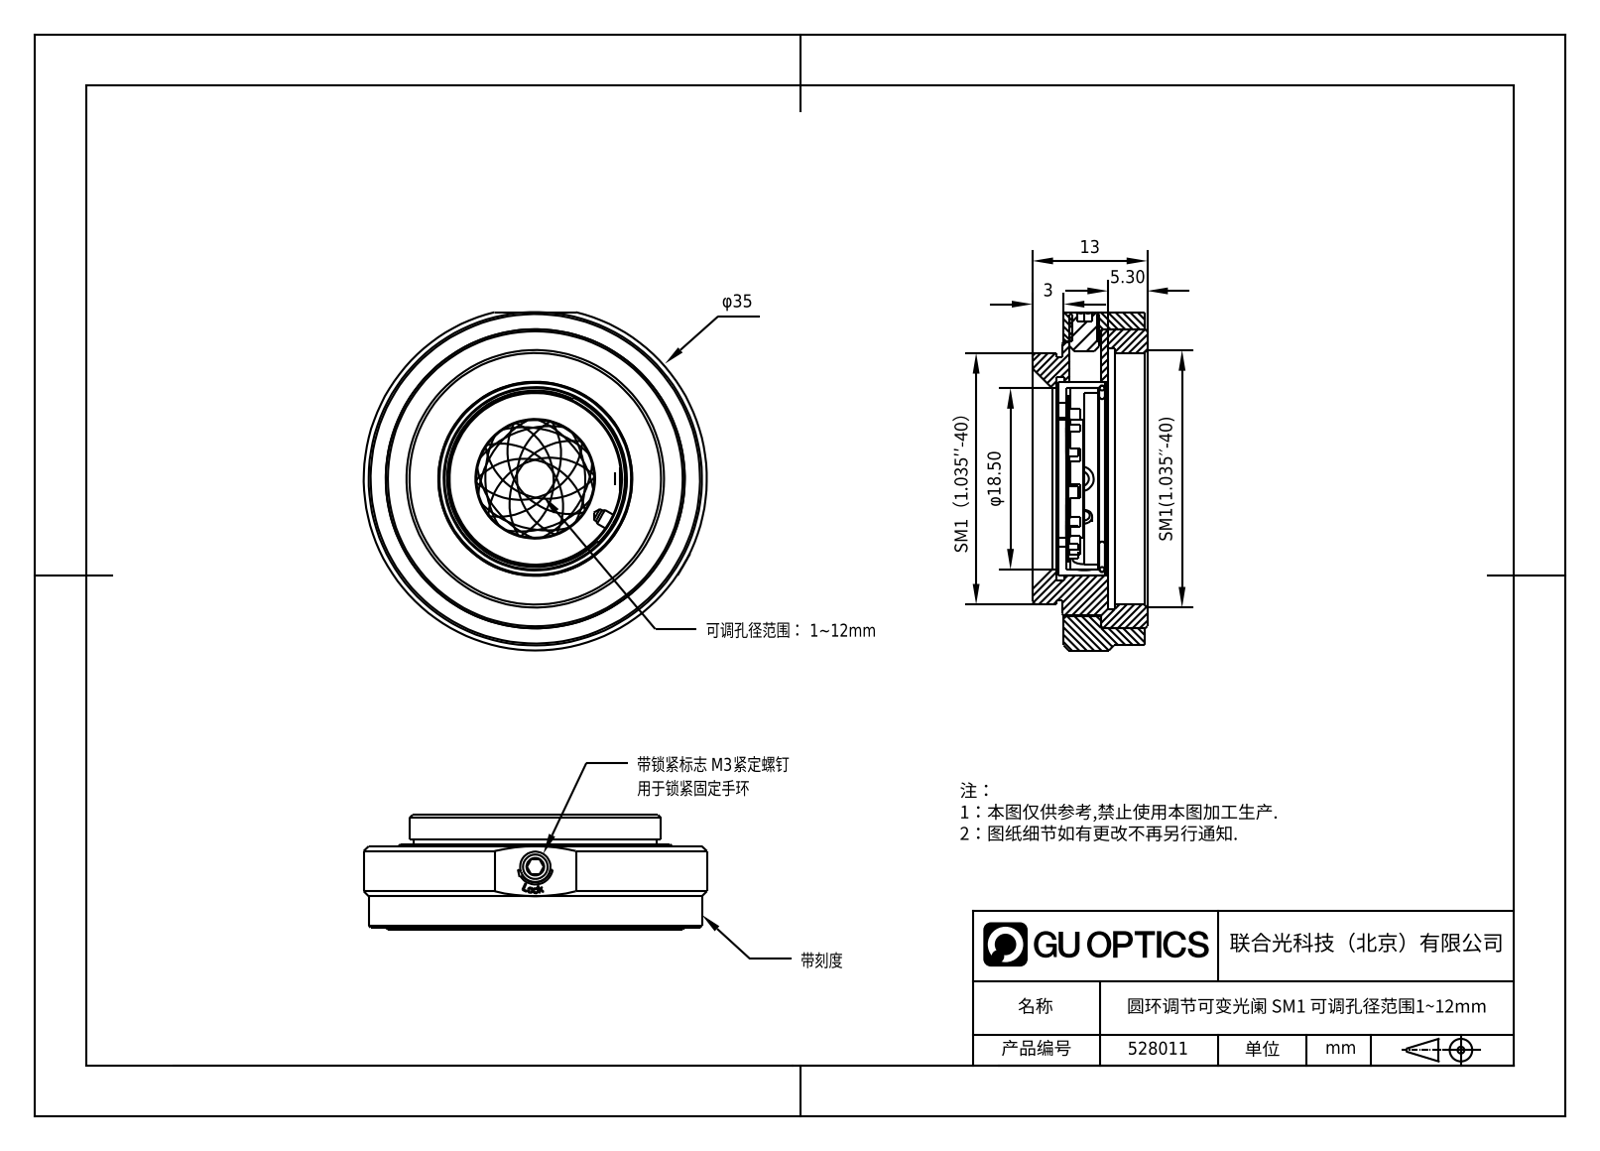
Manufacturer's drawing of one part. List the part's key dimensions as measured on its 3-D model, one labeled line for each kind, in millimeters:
Part name (STEP PRODUCT): SM1螺纹圆环式可调光阑手环，外径35mm，零部件_1.5.2.7.1_ZXL-H1D12B; 1.5.2.7.2_SM1螺纹分度圆环式可调光阑主体，带SM1内外螺纹，外径35mm，零部件，Rev.A; 30.8.1-7，M3尼龙头顶丝_30.8.1_LNJ3*3; 30.5.87-93，LPJ2.5，M2.5不锈钢平头紧定螺丝_30.5.88-PJ2.5*4 (+1 more)
STEP written by: SolidWorks 2021 (CONFIG_CONTROL_DESIGN)
Units: millimetres
Bodies: 4 solids, 1806 faces (256 planar, 384 cylindrical, 1166 other)
Overall size (bounding box): 36.96 × 35 × 13
Volume: 5 097 mm³ · Surface area: 8 851 mm²
Round holes (diameter × count): ⌀1.5 ×2, ⌀1.25 ×1, ⌀2.05 ×1, ⌀2.5 ×1, ⌀2.8 ×1, ⌀12 ×1, ⌀17.5 ×1, ⌀18.5 ×1, ⌀19.8 ×1, ⌀20.8 ×1, ⌀25.66 ×1, ⌀26.66 ×1
Round bosses / shafts (diameter × count): ⌀1.5 ×18, ⌀2 ×2, ⌀35 ×1, ⌀34 ×1, ⌀27.9 ×1, ⌀24.86 ×1, ⌀19.75 ×1, ⌀3 ×1
Partial cylindrical surfaces — rounded edges, fillets, slot ends (radius × count): R6.38 ×10, R1.6 ×5, R1.2 ×2, R1.8 ×1, R13.45 ×1, R16.99 ×1
Main face-to-face distances: 4.5, 0.7, 3.8, 3.5, 9.5, 9.35, 4, 5.3, 4.2, 7.7
Hole centre spacings: 7, 13.99
